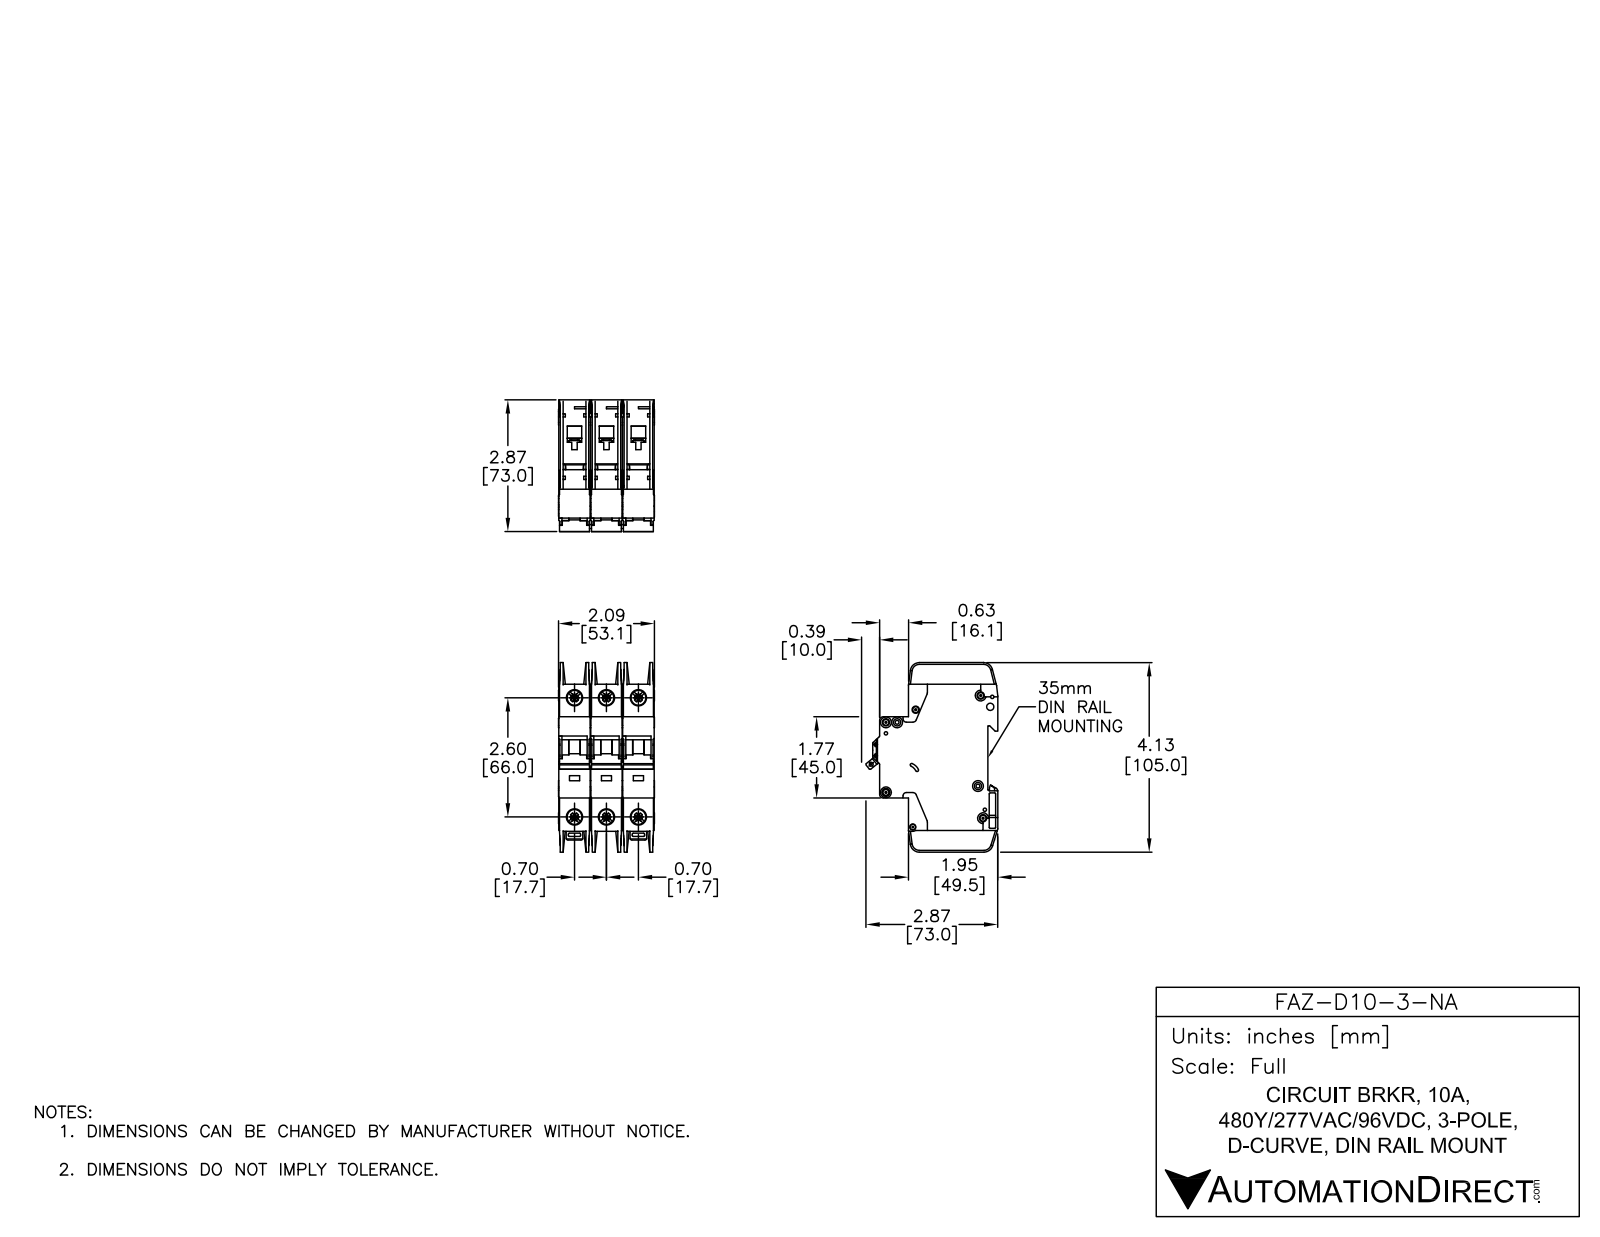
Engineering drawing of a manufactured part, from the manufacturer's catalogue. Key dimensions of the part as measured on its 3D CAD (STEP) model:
Part name (STEP PRODUCT): FAZ-D10-3-NA
STEP written by: SolidWorks 2014 (AUTOMOTIVE_DESIGN)
Units: millimetres
Bodies: 9 solids, 2352 faces (1227 planar, 789 cylindrical, 336 other)
Overall size (bounding box): 105 × 73.04 × 53.1
Volume: 233 085 mm³ · Surface area: 74 219 mm²
Round holes (diameter × count): ⌀3.6 ×7, ⌀7.15 ×6, ⌀8.2 ×6, ⌀1.09 ×2, ⌀1.5 ×2, ⌀4 ×2, ⌀1.9 ×1, ⌀2.15 ×1, ⌀2.2 ×1, ⌀2.55 ×1, ⌀3.3 ×1, ⌀3.4 ×1
Round bosses / shafts (diameter × count): ⌀6 ×7, ⌀2.5 ×3
Partial cylindrical surfaces — rounded edges, fillets, slot ends (radius × count): R0.25 ×65, R0.5 ×30, R1 ×26, R2 ×14, R1.8 ×5, R5 ×5, R4 ×4, R0.2 ×2
Main face-to-face distances: 17.7, 35.4, 17.5, 35.2, 0.7, 15.05, 2.45, 1.75, 15.75, 13.3
Hole centre spacings: 17.7, 68.33, 66, 6.2, 35.4, 74.89, 5.19, 6.1
